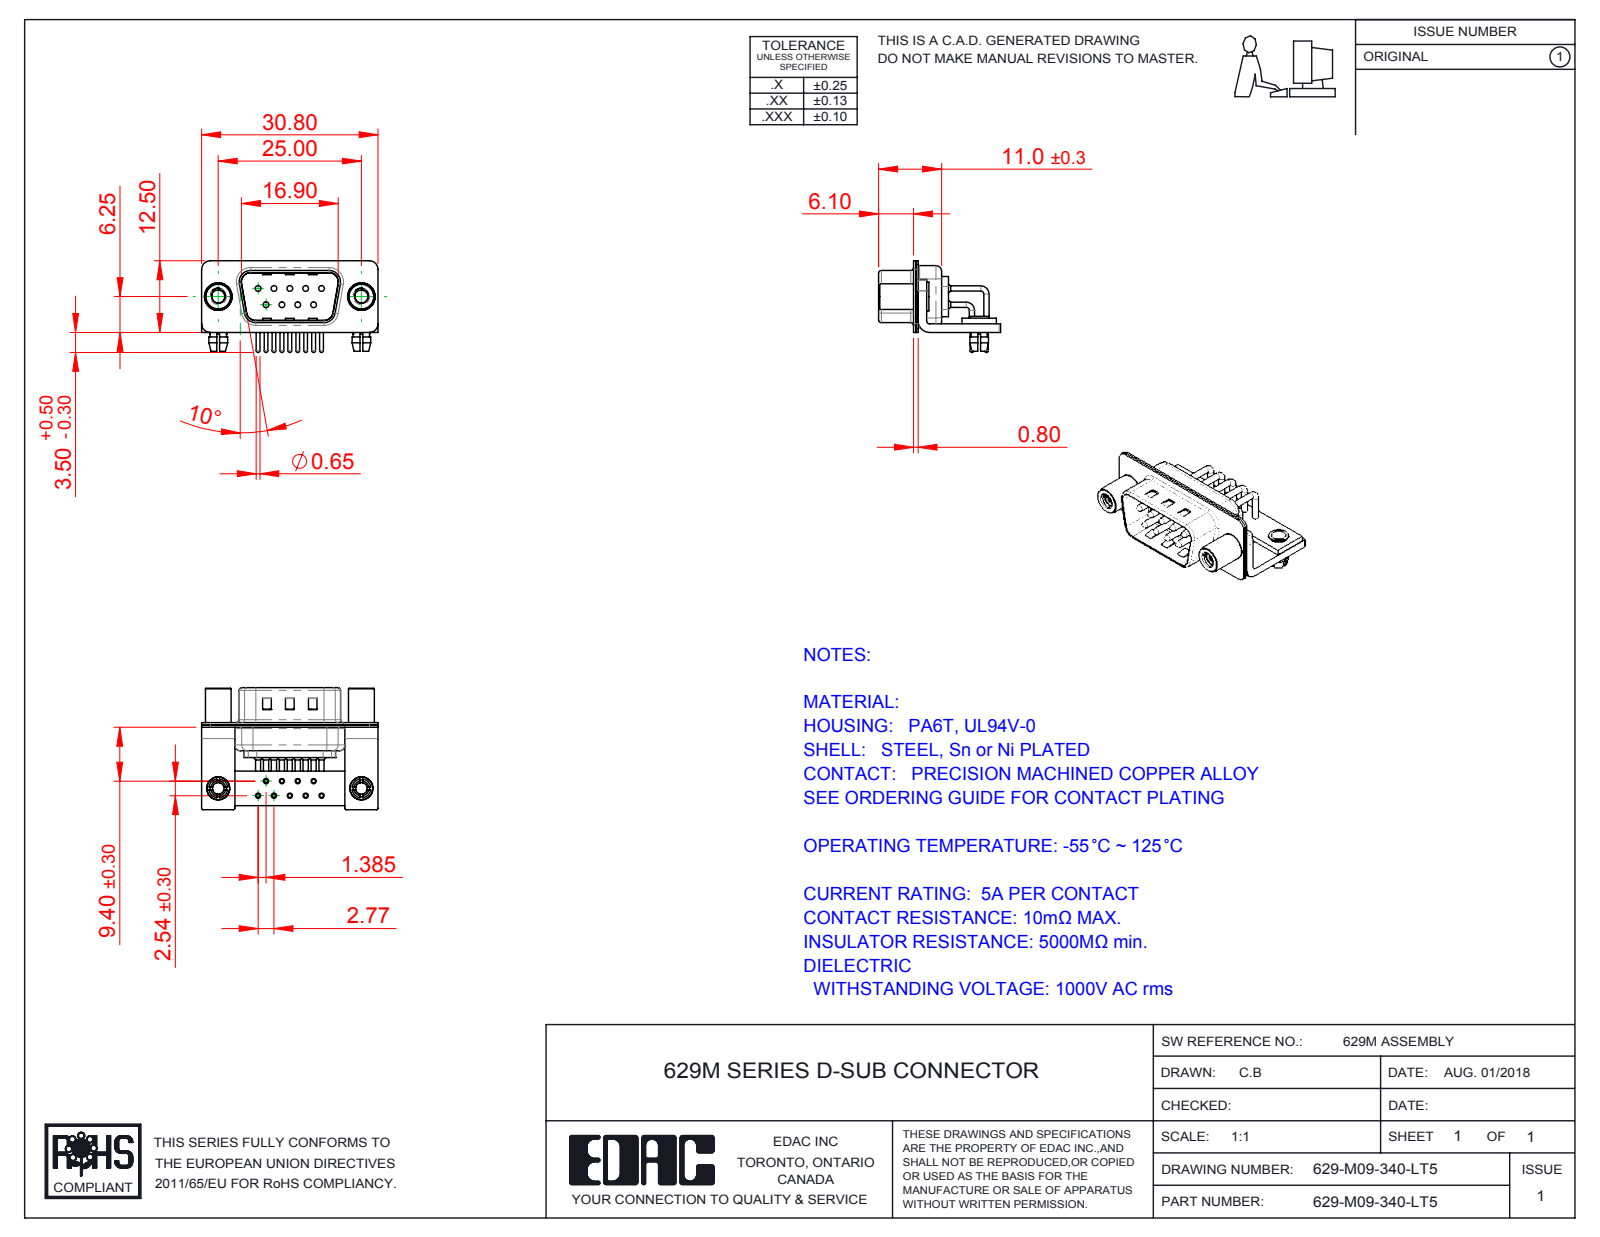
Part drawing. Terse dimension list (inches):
name: 629M Housing_09 Contacts; 629M Shell Front_09 Contacts; 629M Shell Rear_09 Contacts; 629M Contact Row 1 (+6 more)
written by: SolidWorks 2016 (CONFIG_CONTROL_DESIGN)
unit: in
bodies: 19 solids, 1504 faces (759 planar, 567 cylindrical, 178 other)
size: 1.213 × 0.839 × 0.63
volume: 0.121 in³; area: 8.541 in²
holes: 11× ⌀0.079, 9× ⌀0.035, 9× ⌀0.039, 9× ⌀0.067, 2× ⌀0.089, 2× ⌀0.098, 2× ⌀0.126, 2× ⌀0.157, 2× ⌀0.189
bosses: 9× ⌀0.059, 9× ⌀0.035, 9× ⌀0.026, 2× ⌀0.197, 2× ⌀0.193, 2× ⌀0.177, 2× ⌀0.157, 2× ⌀0.134
rounds: 16× R0.01, 16× R0.059, 13× R0.079, 9× R0.02, 9× R0.04, 8× R0.063, 4× R0.024, 4× R0.026
face distances: 0.016, 0.059, 0.031, 0.033, 0.049, 0.075, 0.039, 0.098, 0.409, 0.376
hole spacings: 0.109, 0.218, 0.124, 0.192, 0.327, 0.114, 0.114, 0.198
